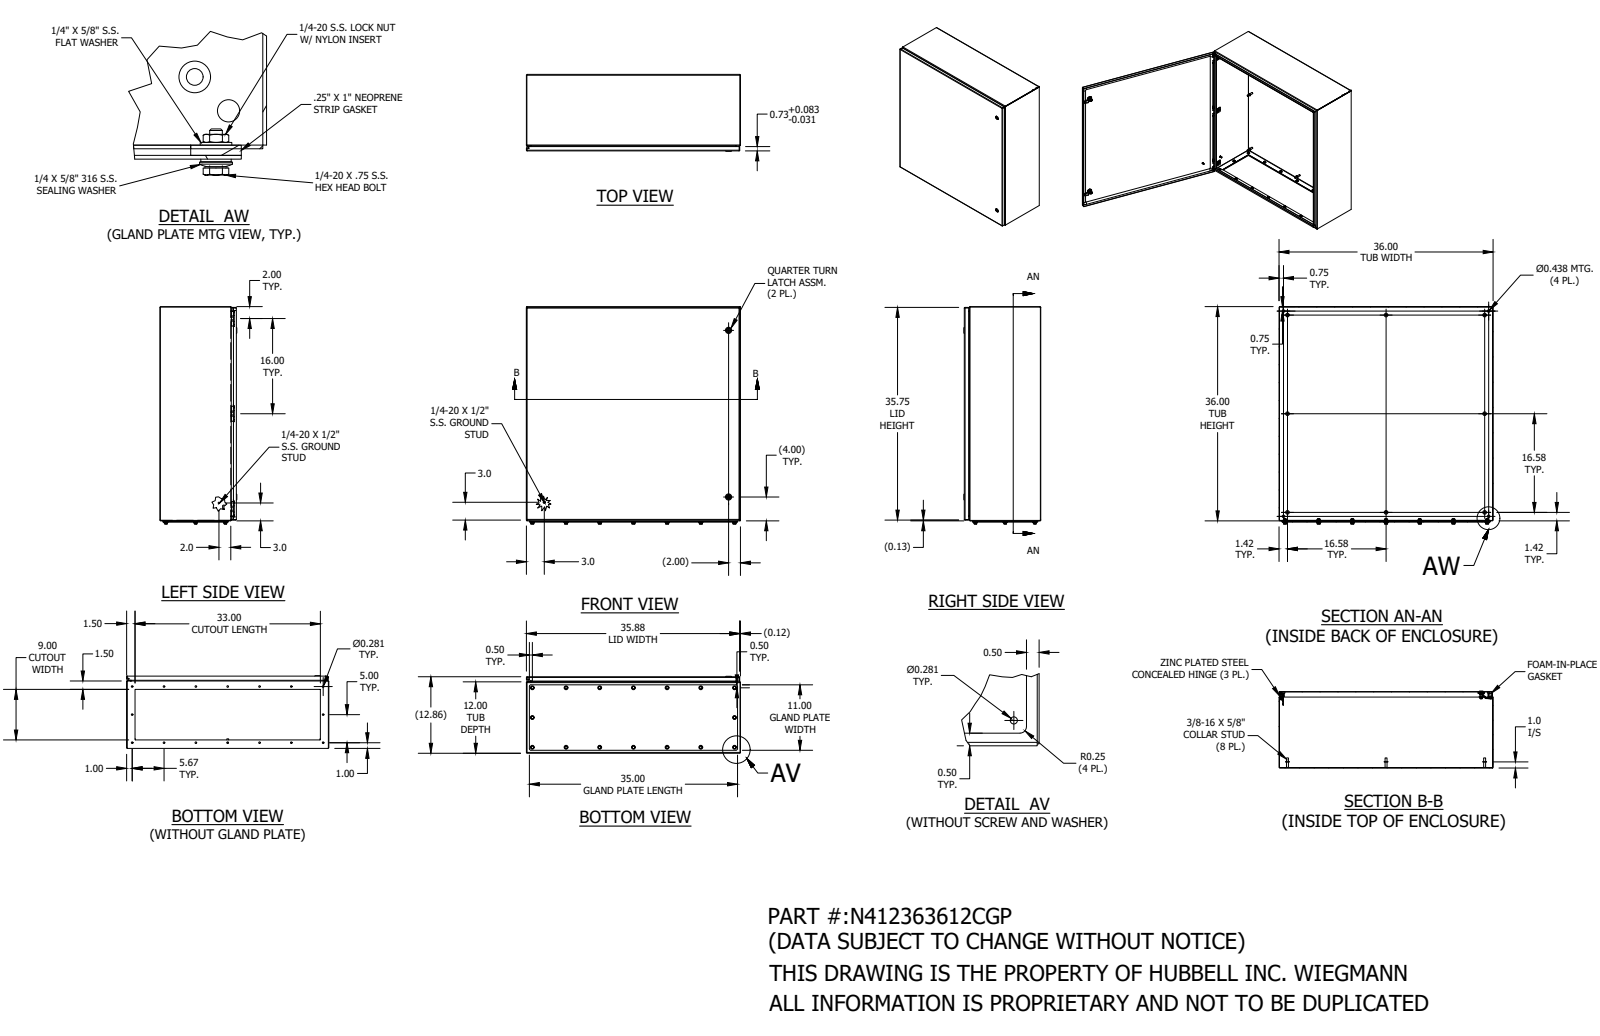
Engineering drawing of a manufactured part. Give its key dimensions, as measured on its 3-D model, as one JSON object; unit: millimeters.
{"part_name": "N412363612CGP", "step_written_by": "SolidWorks 2019 (AUTOMOTIVE_DESIGN)", "units": "millimeters", "bodies": {"solids": 123, "faces": 3333, "planar": 1291, "cylindrical": 1010, "other": 1032}, "overall_size": [927.6, 914.4, 330.5], "volume_mm3": 6406000, "surface_area_mm2": 6411000, "round_holes": [[5.4, 16], [7.1, 16], [7.4, 16], [4.1, 12], [7, 12], [6, 11], [8.9, 9], [4.8, 7], [4.2, 6], [6, 5], [7, 4], [11.1, 4]], "round_bosses_or_shafts": [[6.4, 30], [15.9, 18], [16.5, 16], [15.2, 16], [11.1, 16], [8.4, 8], [15.9, 6], [9.1, 6]], "partial_cylinders_radius": [[0.3, 56], [1.3, 38], [0.5, 21], [3.3, 12], [0.8, 9], [2.7, 9], [4, 9], [3.2, 6]], "face_to_face_distances": [1.9, 324.6, 322.8, 326.5, 912.5, 917.7, 910.6, 914.4, 915.8, 919.6], "hole_center_spacings": [406.4, 143.9, 287.9, 291.9, 383.9, 431.8, 501, 812.8]}
